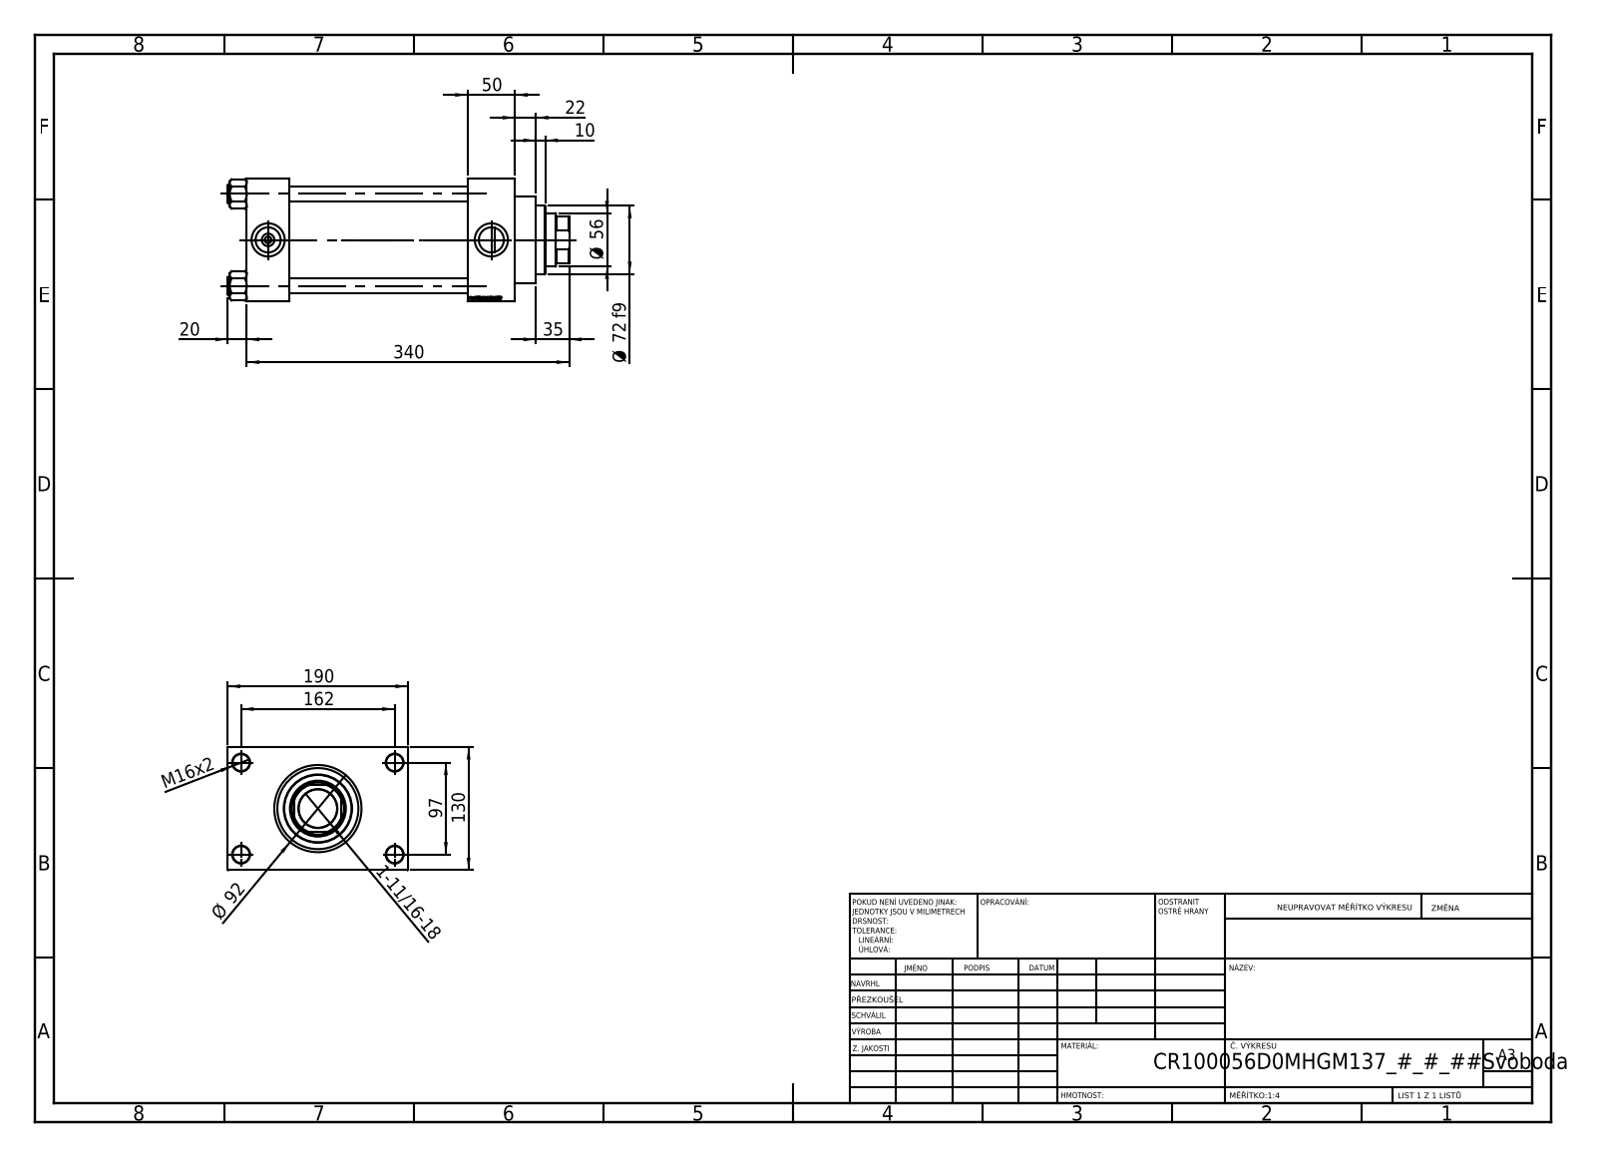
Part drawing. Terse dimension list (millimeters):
name: V215CR_D_Body; V215CR_D_TYCINKA; NUT_M5_D; V215CR_VCP_D (+1 more)
written by: SolidWorks 2019 (CONFIG_CONTROL_DESIGN)
unit: mm
bodies: 11 solids, 1151 faces (545 planar, 88 cylindrical, 518 other)
size: 360 × 190 × 130
volume: 3 124 000 mm³; area: 482 190 mm²
holes: 4× ⌀16, 4× ⌀18, 2× ⌀7, 2× ⌀26.44, 2× ⌀35, 1× ⌀40.5, 1× ⌀56, 1× ⌀59, 1× ⌀76, 1× ⌀85.5, 1× ⌀100
bosses: 4× ⌀19, 1× ⌀106, 1× ⌀92, 1× ⌀72
rounds: 1× R27
face distances: 130, 50, 45, 188, 233, 283, 238, 30, 160, 190
hole spacings: 32.55, 68.52, 94.41, 96.9, 102.27, 129.45, 161.73, 97
